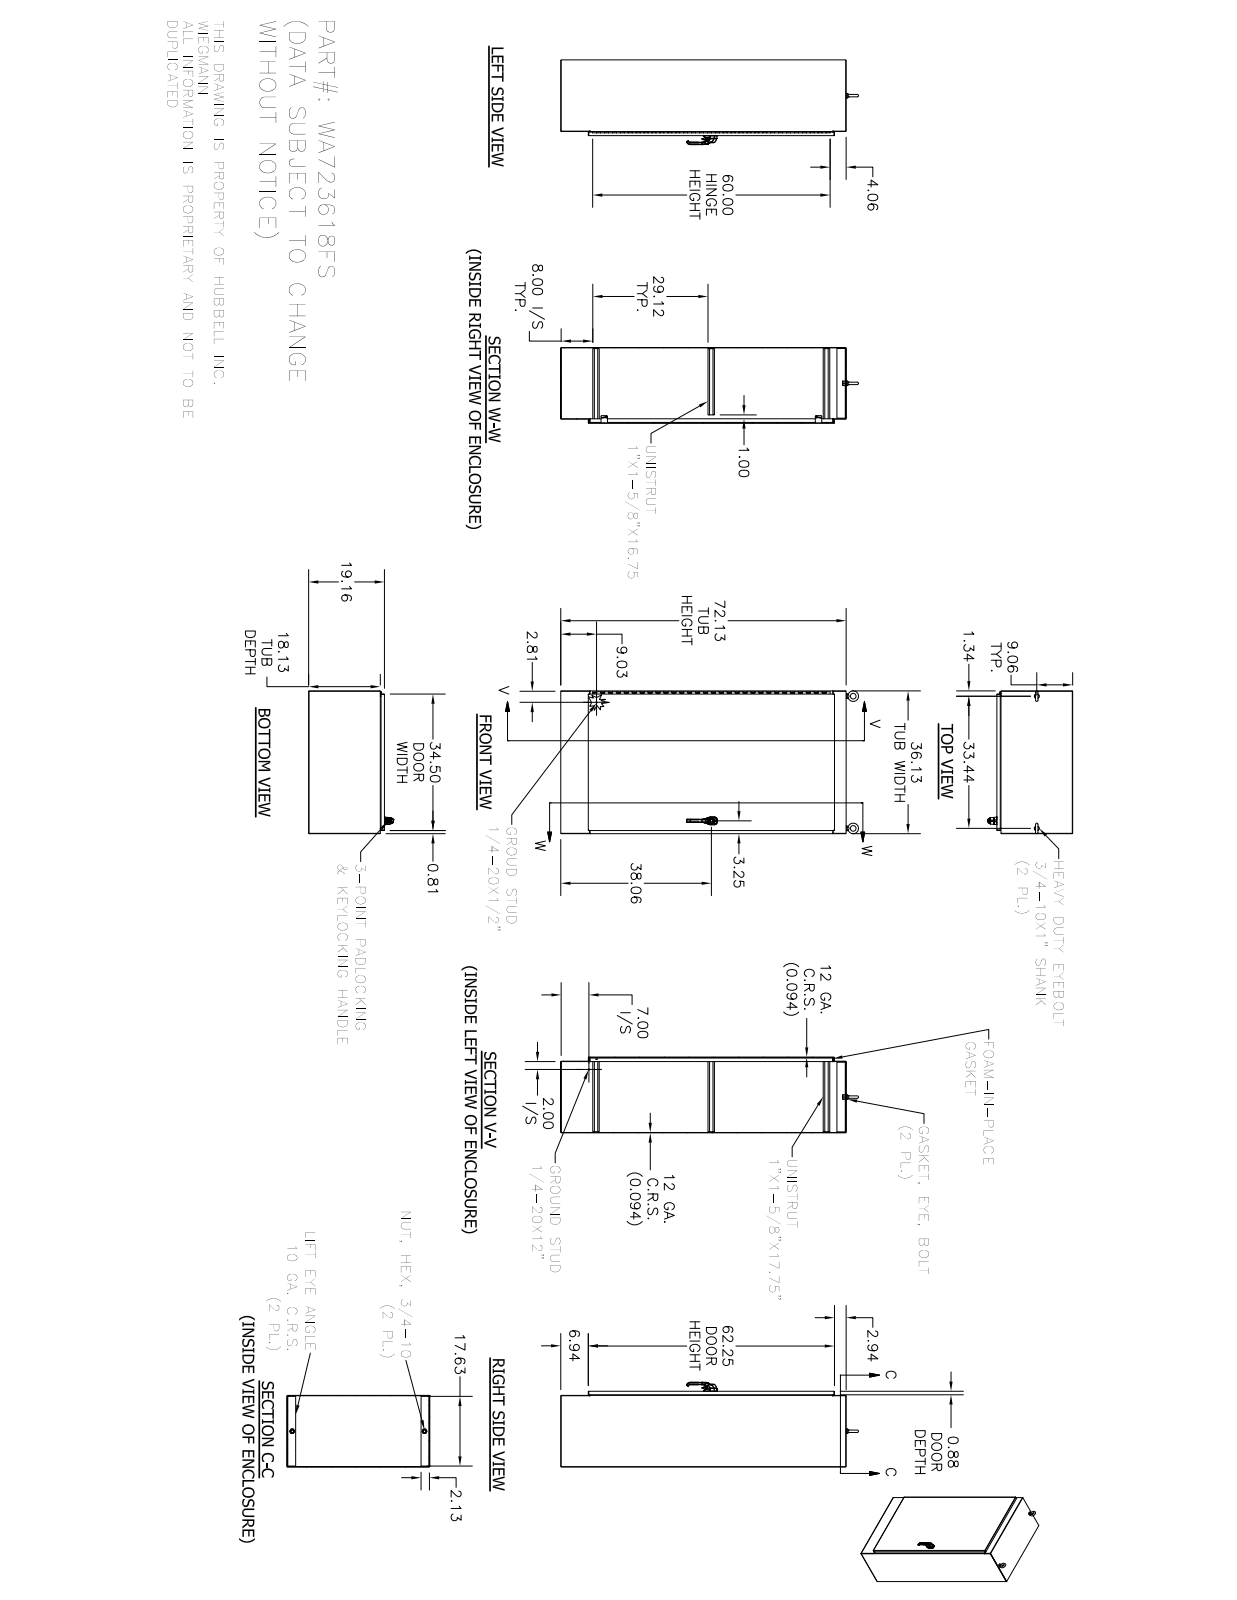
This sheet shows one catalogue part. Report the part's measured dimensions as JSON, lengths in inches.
{"part_name": "WA723618FSBLS; WA7218FSRS; WA3618FSTOP; WA3618FSBTM (+8 more)", "step_written_by": "Autodesk Inventor 2014 (AUTOMOTIVE_DESIGN)", "units": "inches", "bodies": {"solids": 46, "faces": 2855, "planar": 1212, "cylindrical": 995, "other": 648}, "overall_size": [75.248, 36.125, 21.409], "volume_in3": 972.7, "surface_area_in2": 20650, "round_holes": [[0.276, 8], [0.2, 4], [0.213, 3], [0.28, 3], [0.315, 2], [0.402, 2], [0.407, 2], [0.413, 2], [0.642, 2], [0.813, 2], [0.122, 1], [0.124, 1]], "round_bosses_or_shafts": [[0.25, 3], [1.25, 2], [1.12, 2], [0.75, 2], [0.531, 2], [0.526, 2], [0.435, 2], [0.337, 2]], "partial_cylinders_radius": [[0.02, 170], [0.012, 100], [0.019, 21], [0.01, 16], [0.031, 15], [0.079, 14], [0.125, 13], [0.019, 12]], "face_to_face_distances": [0.094, 19.067, 36.031, 18.973, 19.161, 35.938, 72.031, 36.125, 18.031, 1.035], "hole_center_spacings": [0.38, 0.382, 0.382, 0.762, 0.764, 0.886, 1.144, 1.271]}
